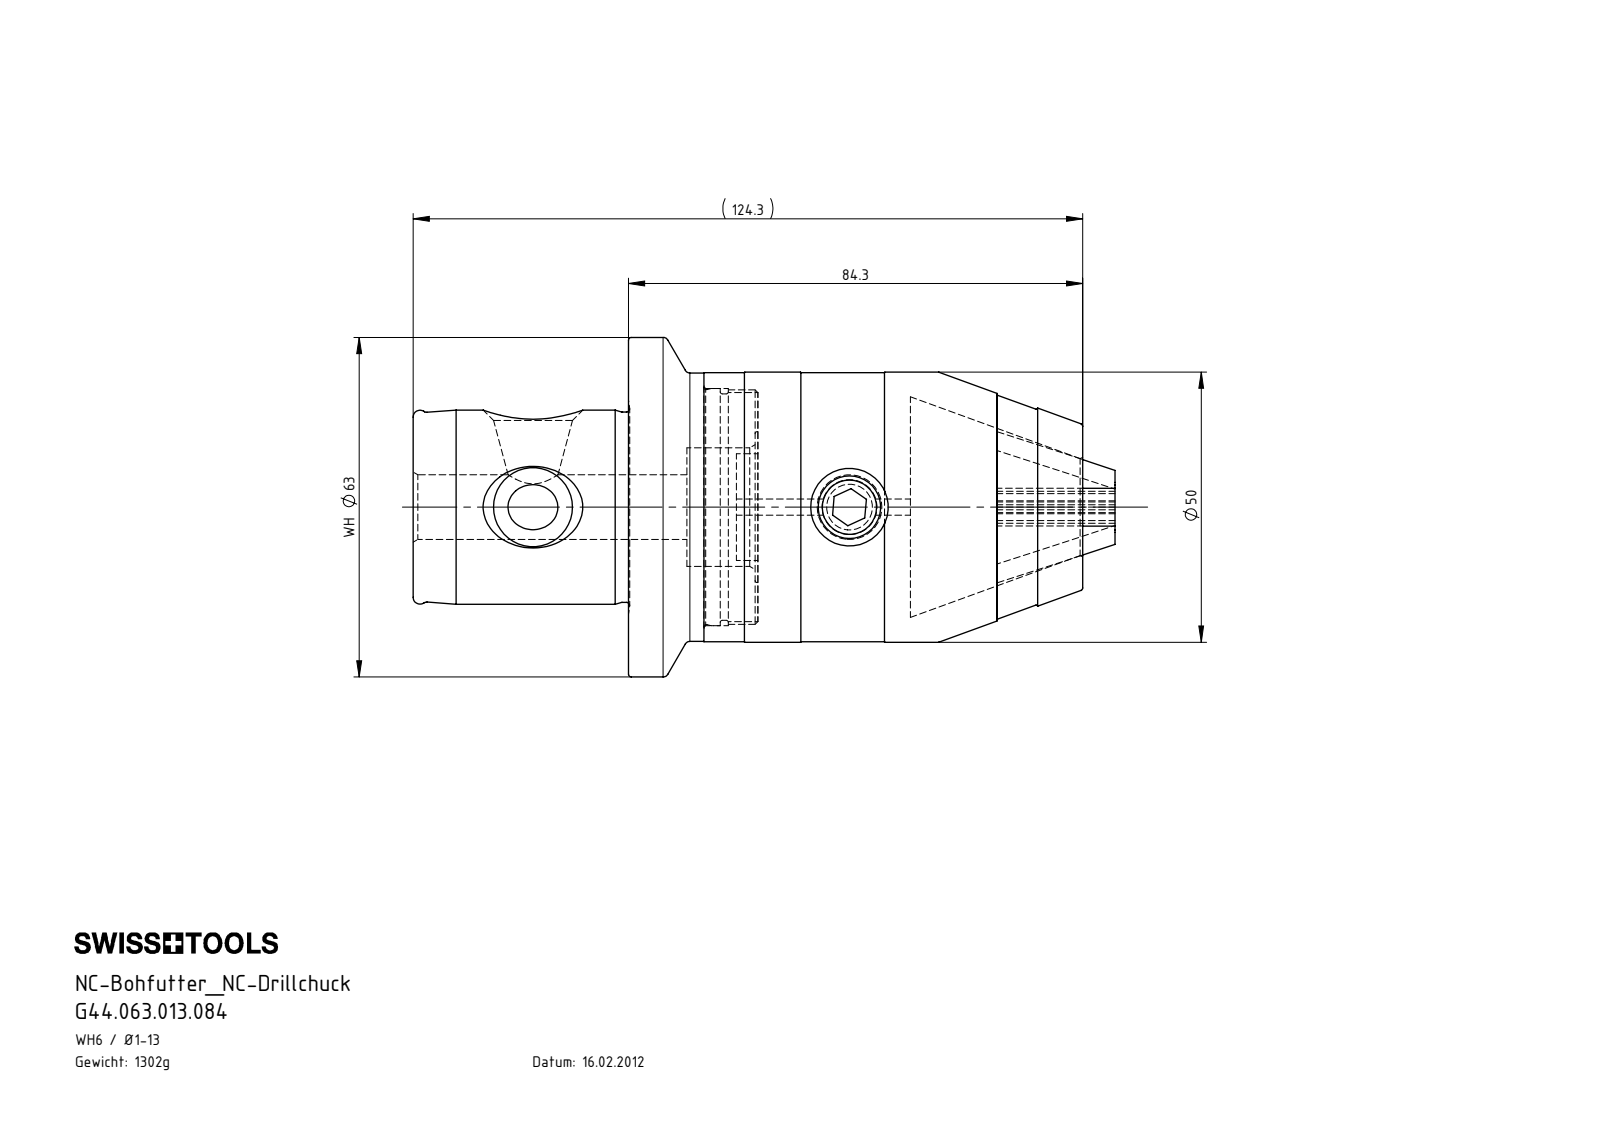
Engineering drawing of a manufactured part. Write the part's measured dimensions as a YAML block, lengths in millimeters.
part_name: "WH6.BF1.K01.084; ISO 4026 - M12 x 20; Backe ø1-13; WH6-BF2.K01.014 (+2 more)"
step_written_by: "SolidWorks 2022 (AUTOMOTIVE_DESIGN)"
units: millimeters
bodies: {solids: 6, faces: 215, planar: 57, cylindrical: 58, other: 100}
overall_size: [130.3, 63, 63]
volume: 165910
surface_area: 40831
round_holes:
  - {diameter: 3, count: 1}
  - {diameter: 10.2, count: 1}
  - {diameter: 12, count: 1}
  - {diameter: 14.4, count: 1}
  - {diameter: 22, count: 1}
  - {diameter: 28, count: 1}
  - {diameter: 42.5, count: 1}
  - {diameter: 44, count: 1}
round_bosses_or_shafts:
  - {diameter: 63, count: 1}
  - {diameter: 50.1, count: 1}
  - {diameter: 49.9, count: 1}
  - {diameter: 49.8, count: 1}
  - {diameter: 43.6, count: 1}
  - {diameter: 43.5, count: 1}
  - {diameter: 42, count: 1}
  - {diameter: 36, count: 1}
partial_cylinders:
  - {radius: 0.3, count: 6}
  - {radius: 0.5, count: 6}
face_to_face_distances: [52.3, 24, 28.3, 23.97, 28.33, 14, 9.97, 10, 38.3, 40]
